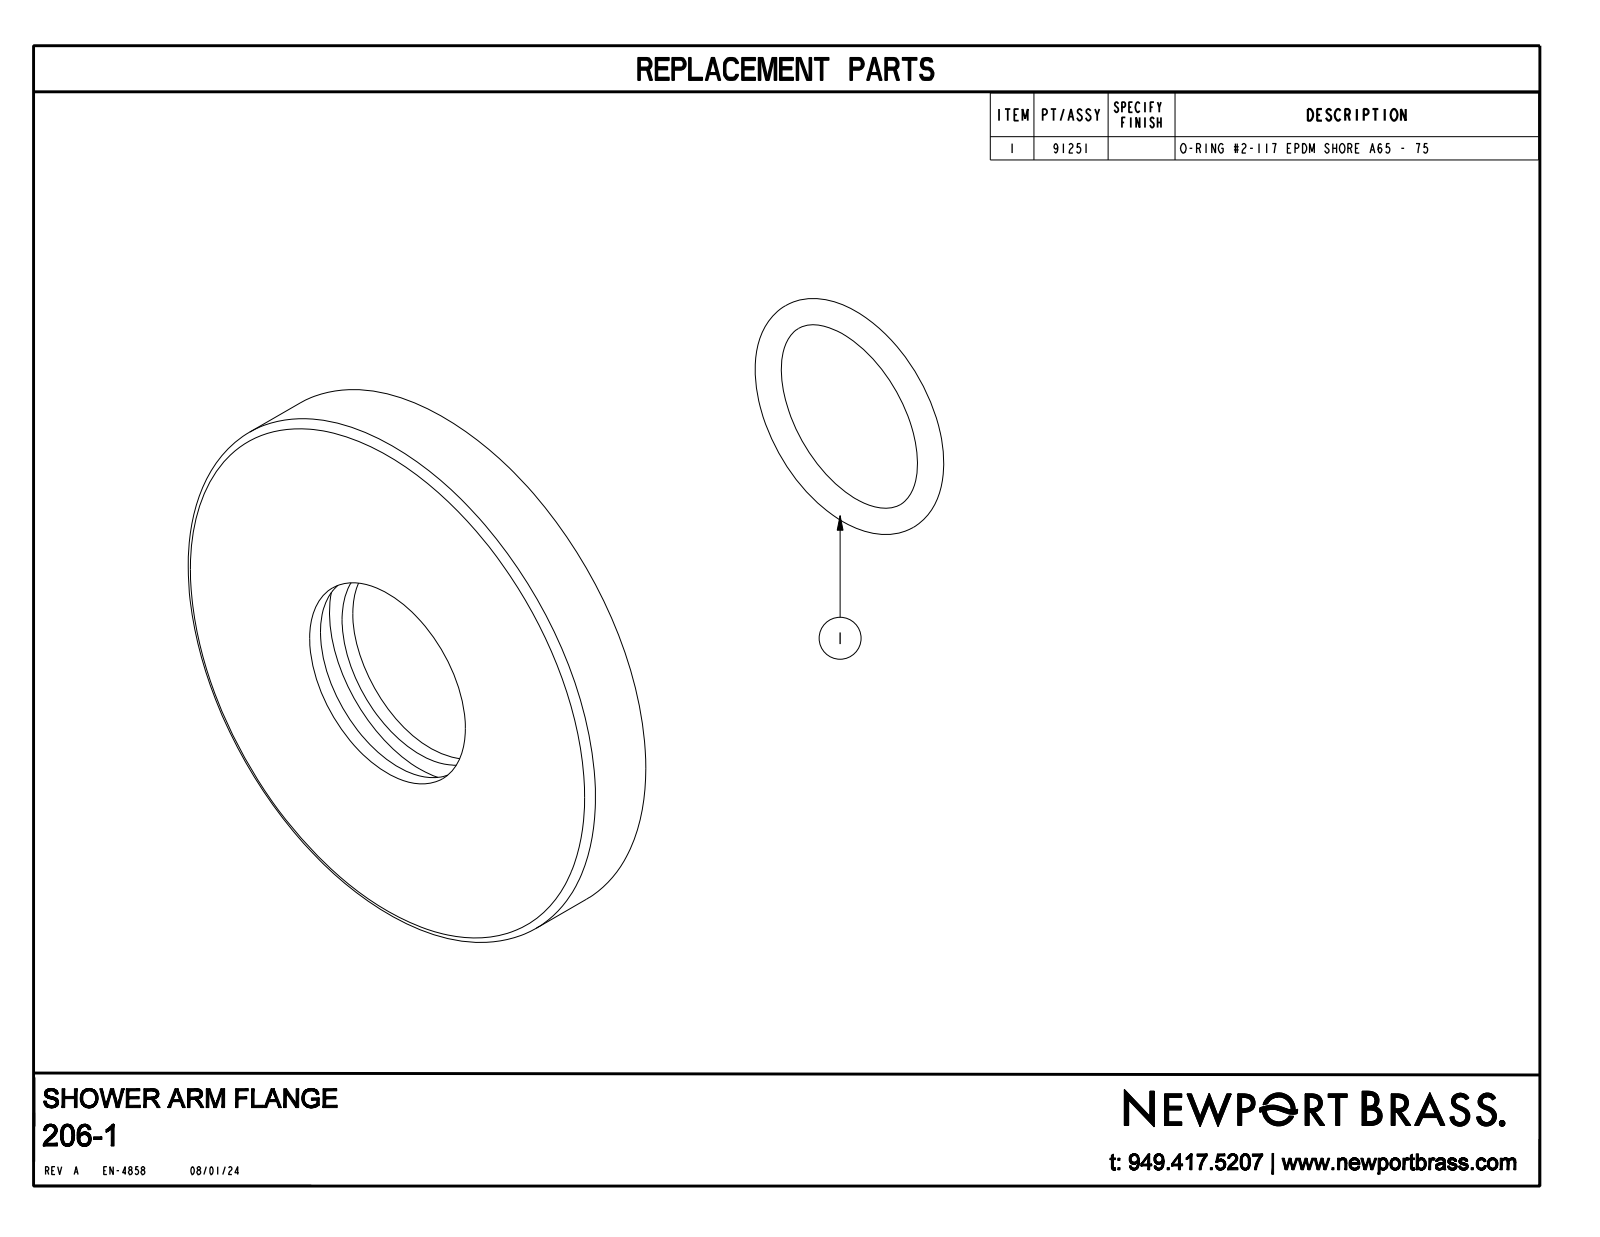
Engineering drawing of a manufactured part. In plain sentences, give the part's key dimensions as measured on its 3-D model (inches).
The part is named "11754". Its 3-D file was written by "PRO/ENGINEER BY PARAMETRIC TECHNOLOGY CORPORATION, 2013150 (CONFIG_CONTROL_DESIGN)". It is 1 solid with 22 faces: 6 planar, 12 cylindrical and 4 other. Overall it measures 2.25 by 2.25 by 0.31 inches. Its volume is 0.846 cubic inches and its surface area 15.92 square inches. Round holes: 1 of diameter 0.865, 1 of diameter 1.005, 1 of diameter 2. Round bosses or shafts: 1 of diameter 2.25. The main face-to-face distances are 0.24, 0.07, 0.31, 0.13, 0.25, 0.06, 0.18, 0.12, 0.18, 0.06.
